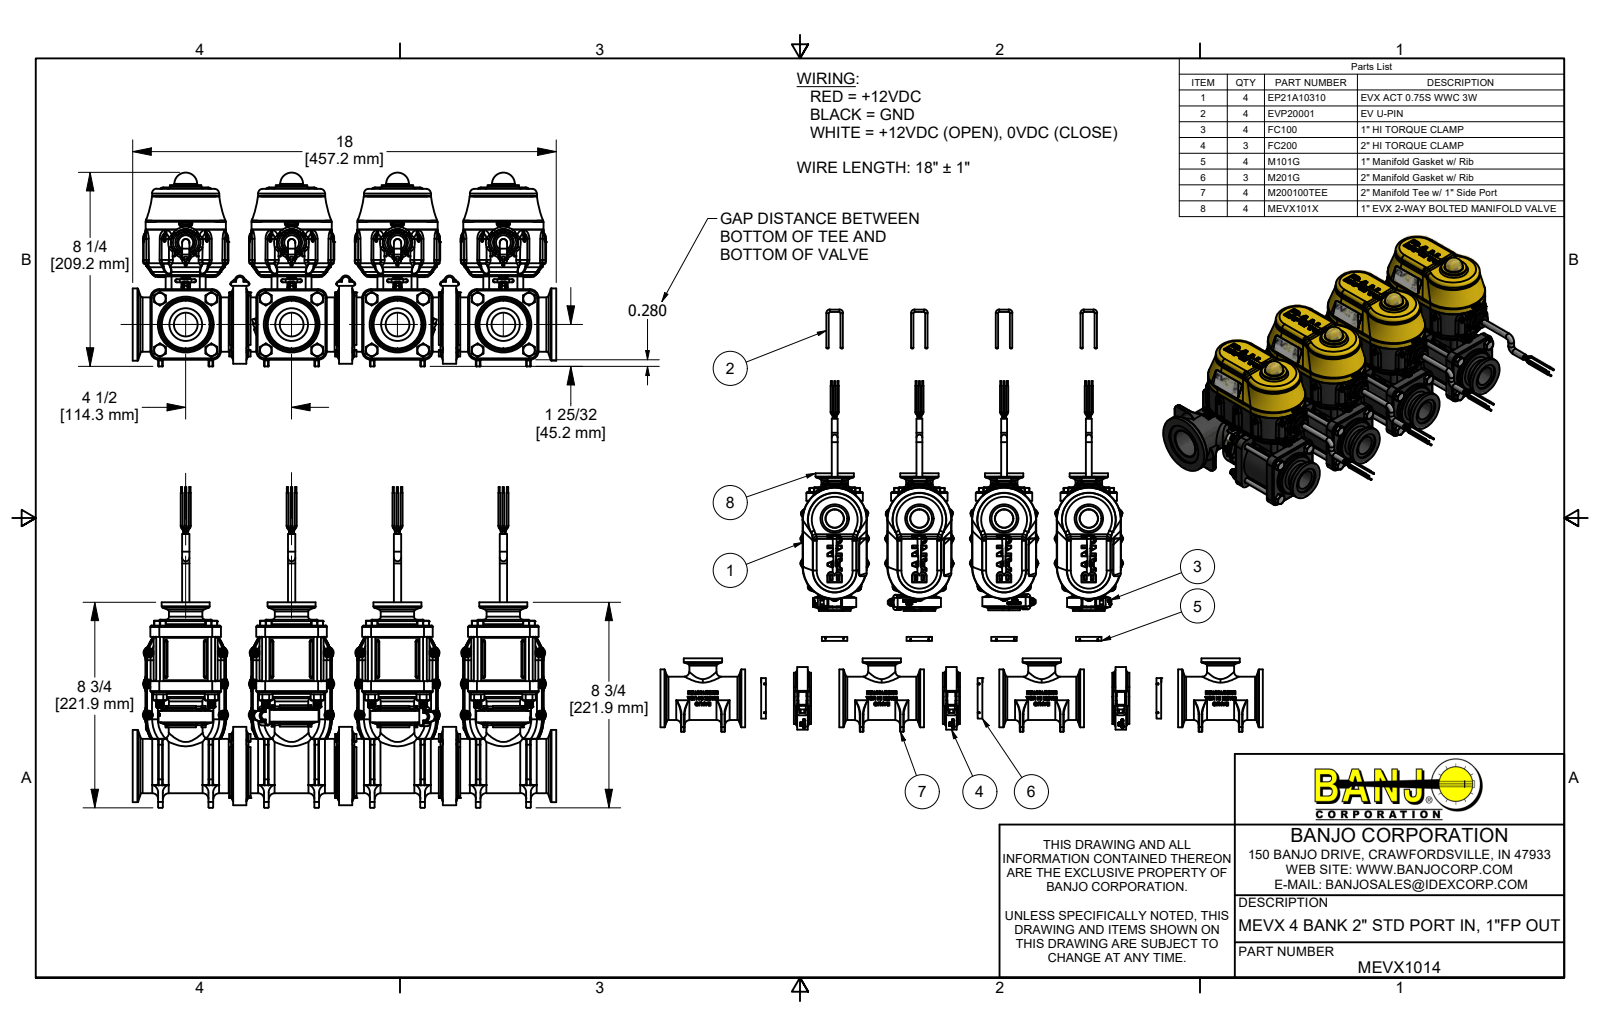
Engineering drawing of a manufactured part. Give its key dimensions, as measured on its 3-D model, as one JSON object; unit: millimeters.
{"part_name": "MEVX1014; EP21A10310; EP10310; IRF4905 (+8 more)", "step_written_by": "Autodesk Inventor 2019 (AUTOMOTIVE_DESIGN)", "units": "millimeters", "bodies": {"solids": 402, "faces": 49987, "planar": 12988, "cylindrical": 14632, "other": 22367}, "overall_size": [457.2, 346.1, 209.2], "volume_mm3": 4436000, "surface_area_mm2": 1901000, "round_holes": [[2.4, 44], [3.8, 44], [2, 28], [2.7, 16], [3.2, 16], [3.5, 16], [3.8, 16], [3.8, 16], [4.3, 16], [6.4, 16], [8.2, 16], [8.9, 16]], "round_bosses_or_shafts": [[6.8, 240], [6.4, 68], [2, 60], [3.6, 44], [2.7, 44], [2.2, 44], [1.5, 24], [8, 20]], "partial_cylinders_radius": [[0.3, 720], [1, 580], [0.3, 341], [0.8, 259], [0.5, 228], [0.1, 176], [1.5, 148], [2, 112]], "face_to_face_distances": [114.3, 2.5, 228.6, 65.2, 12.2, 5.4, 1.5, 3.8, 60.1, 89], "hole_center_spacings": [114.3, 228.6, 42.2, 67.5, 68.3, 69, 342.9, 114.3]}
